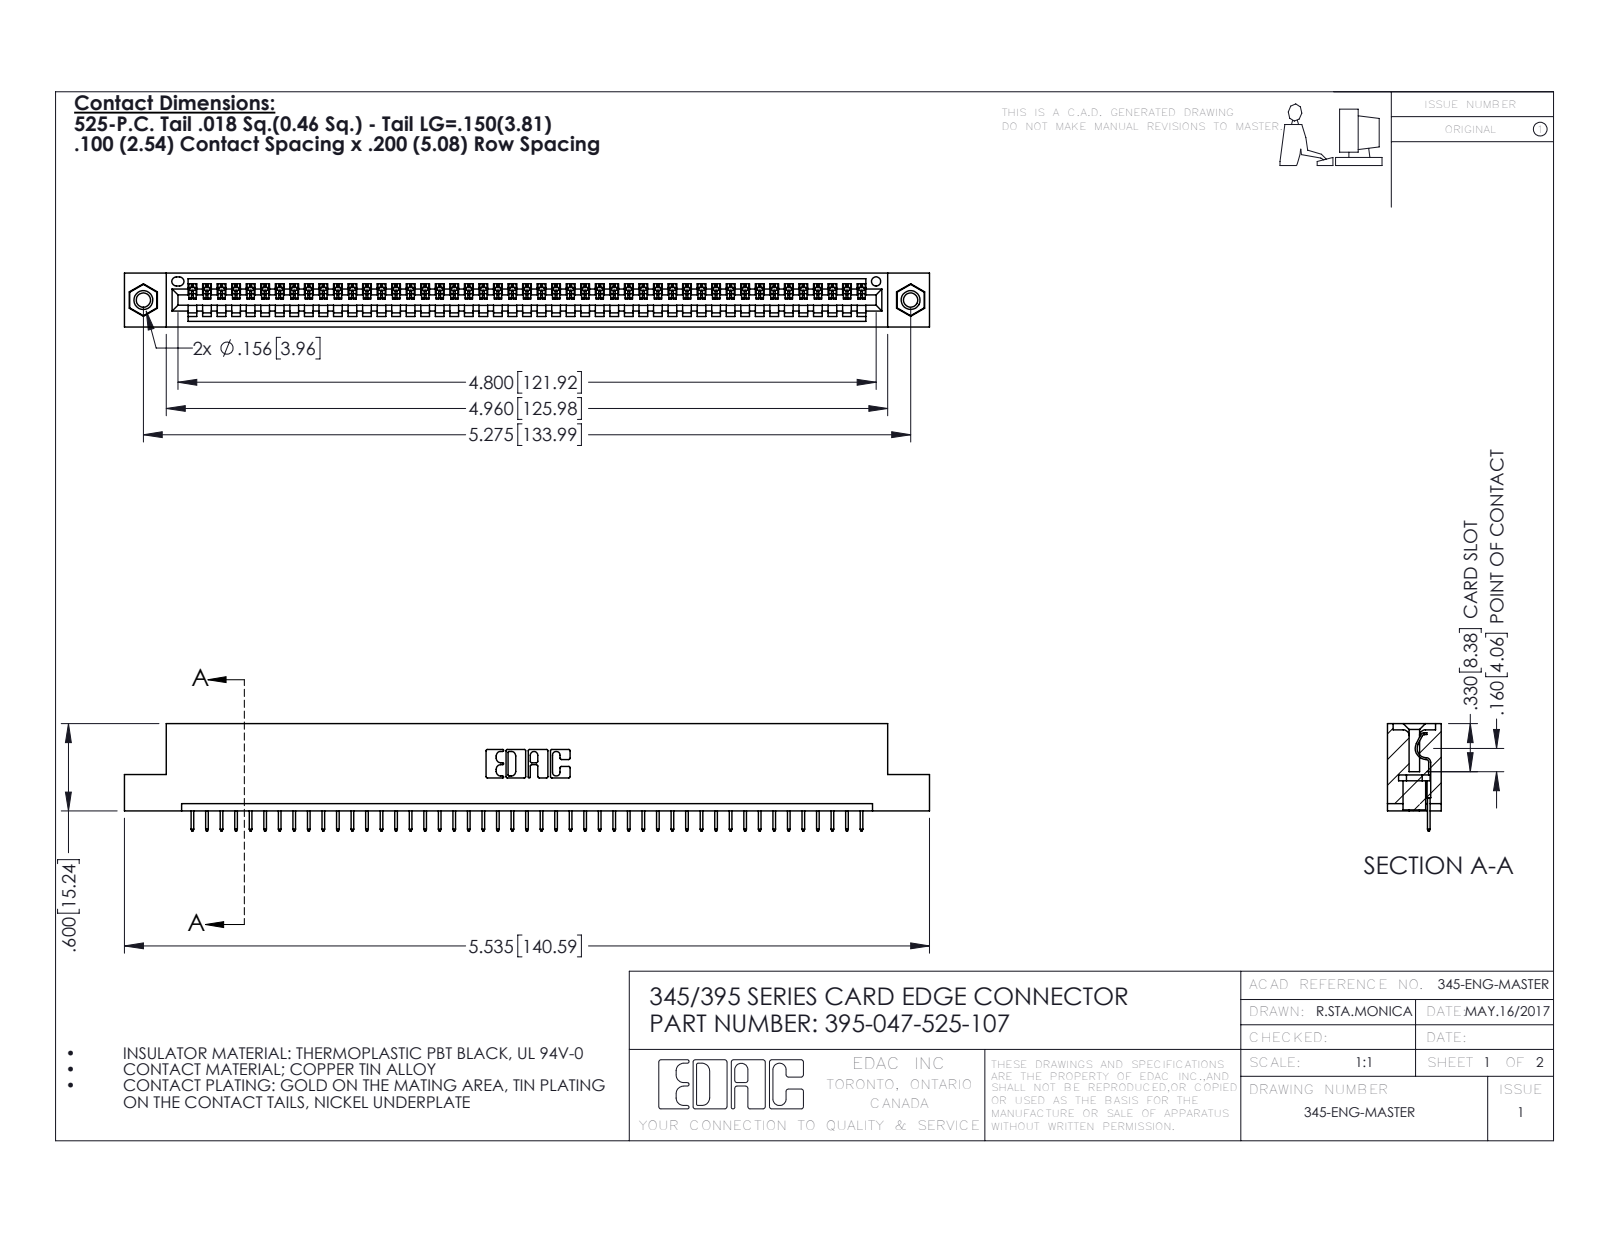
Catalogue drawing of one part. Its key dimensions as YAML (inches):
part_name: "345-292-001_345-293-125; 345-250-001_345-250-005-103; 395-047-525-107; 345 Part_Flush Mounting Lugs - 0.156 Dia-TI"
step_written_by: "SolidWorks 2020 (CONFIG_CONTROL_DESIGN)"
units: inches
bodies: {solids: 50, faces: 3100, planar: 2274, cylindrical: 810, other: 16}
overall_size: [5.535, 0.737, 0.37]
volume: 0.805
surface_area: 26.33
round_holes:
  - {diameter: 0.098, count: 2}
  - {diameter: 0.125, count: 2}
  - {diameter: 0.156, count: 2}
  - {diameter: 0.064, count: 1}
round_bosses_or_shafts:
  - {diameter: 0.155, count: 2}
partial_cylinders:
  - {radius: 0.006, count: 94}
  - {radius: 0.01, count: 22}
  - {radius: 0.007, count: 6}
  - {radius: 0.031, count: 6}
  - {radius: 0.026, count: 3}
  - {radius: 0.031, count: 2}
  - {radius: 0.04, count: 2}
  - {radius: 0.014, count: 1}
face_to_face_distances: [0.072, 0.298, 0.37, 0.2, 0.098, 0.272, 0.025, 0.225, 0.072, 0.149]
hole_center_spacings: [0.27, 5.039, 5.275]
